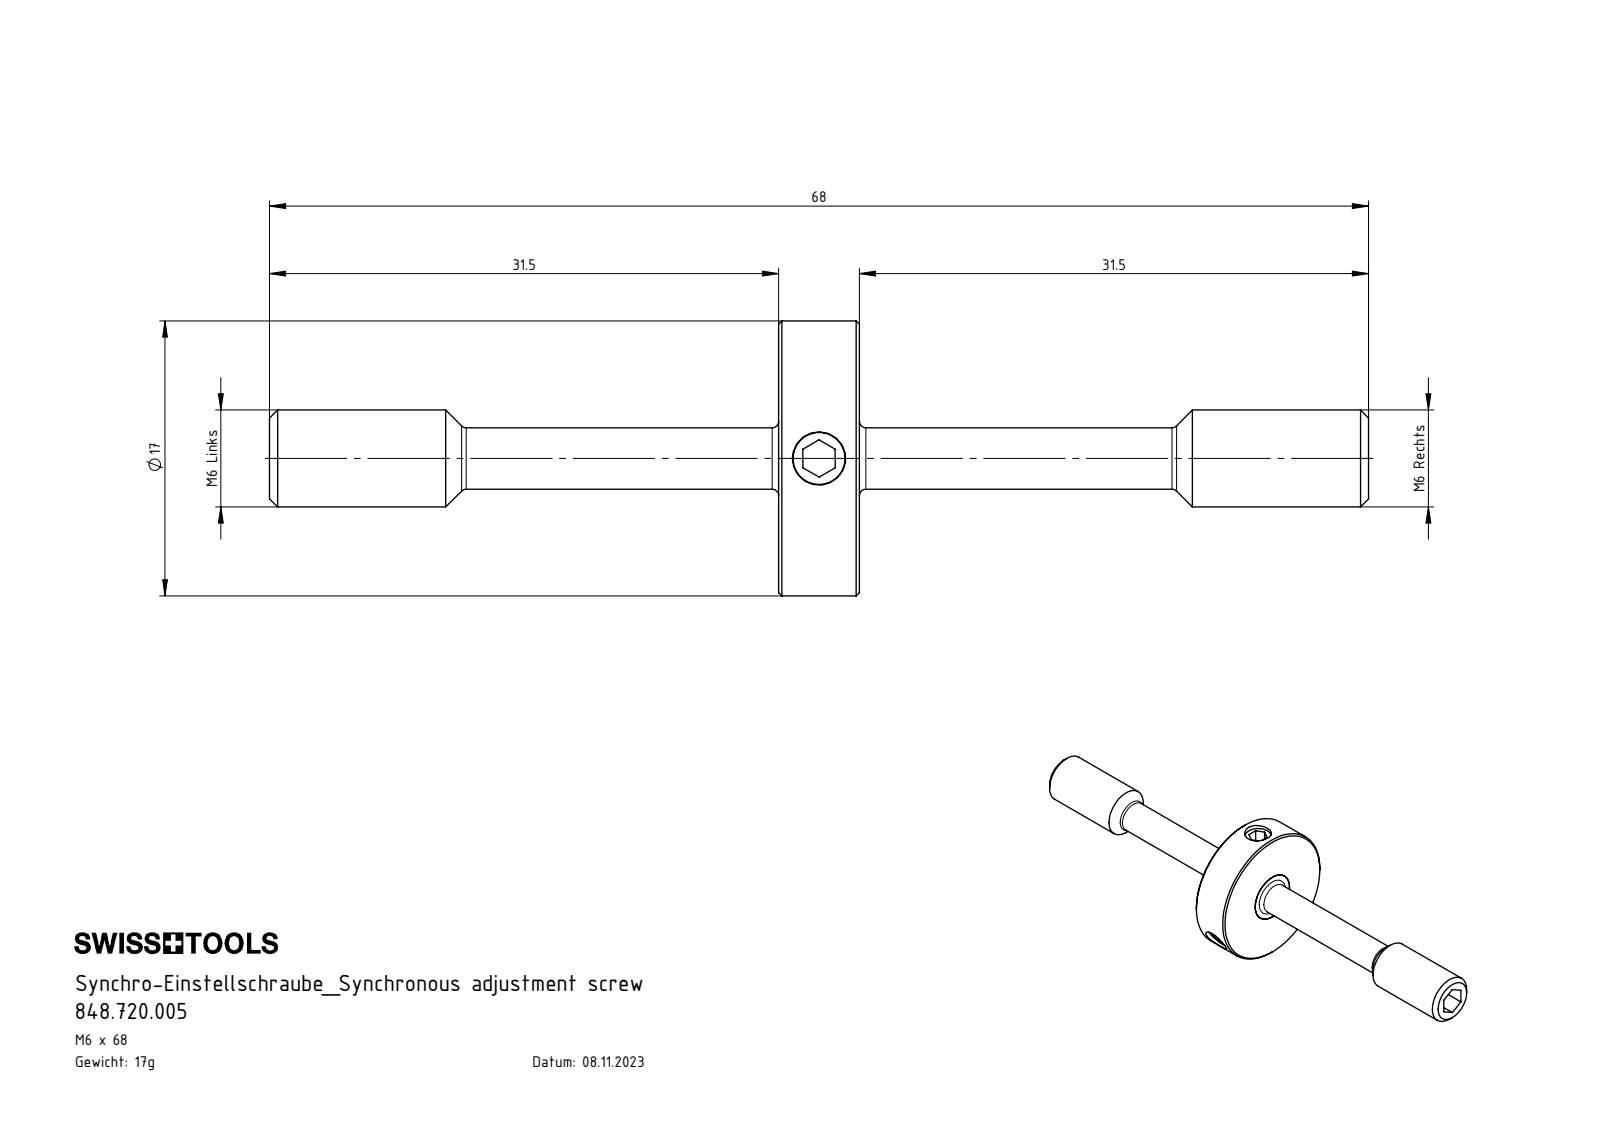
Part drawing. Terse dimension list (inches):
name: ISO 4026 - M4 x 5; Z72-ER3.001.068_A; 848.720.005; Z42-ER3.002.005_A
written by: SolidWorks 2022 (AUTOMOTIVE_DESIGN)
unit: in
bodies: 5 solids, 99 faces (39 planar, 26 cylindrical, 34 other)
size: 2.677 × 0.669 × 0.669
volume: 0.135 in³; area: 3.542 in²
holes: 3× ⌀0.13
bosses: 3× ⌀0.157, 1× ⌀0.669, 1× ⌀0.236, 1× ⌀0.15
face distances: 0.197, 1.24, 1.437, 0.079, 0.098, 0.118, 2.677, 1.299, 1.378, 0.059
